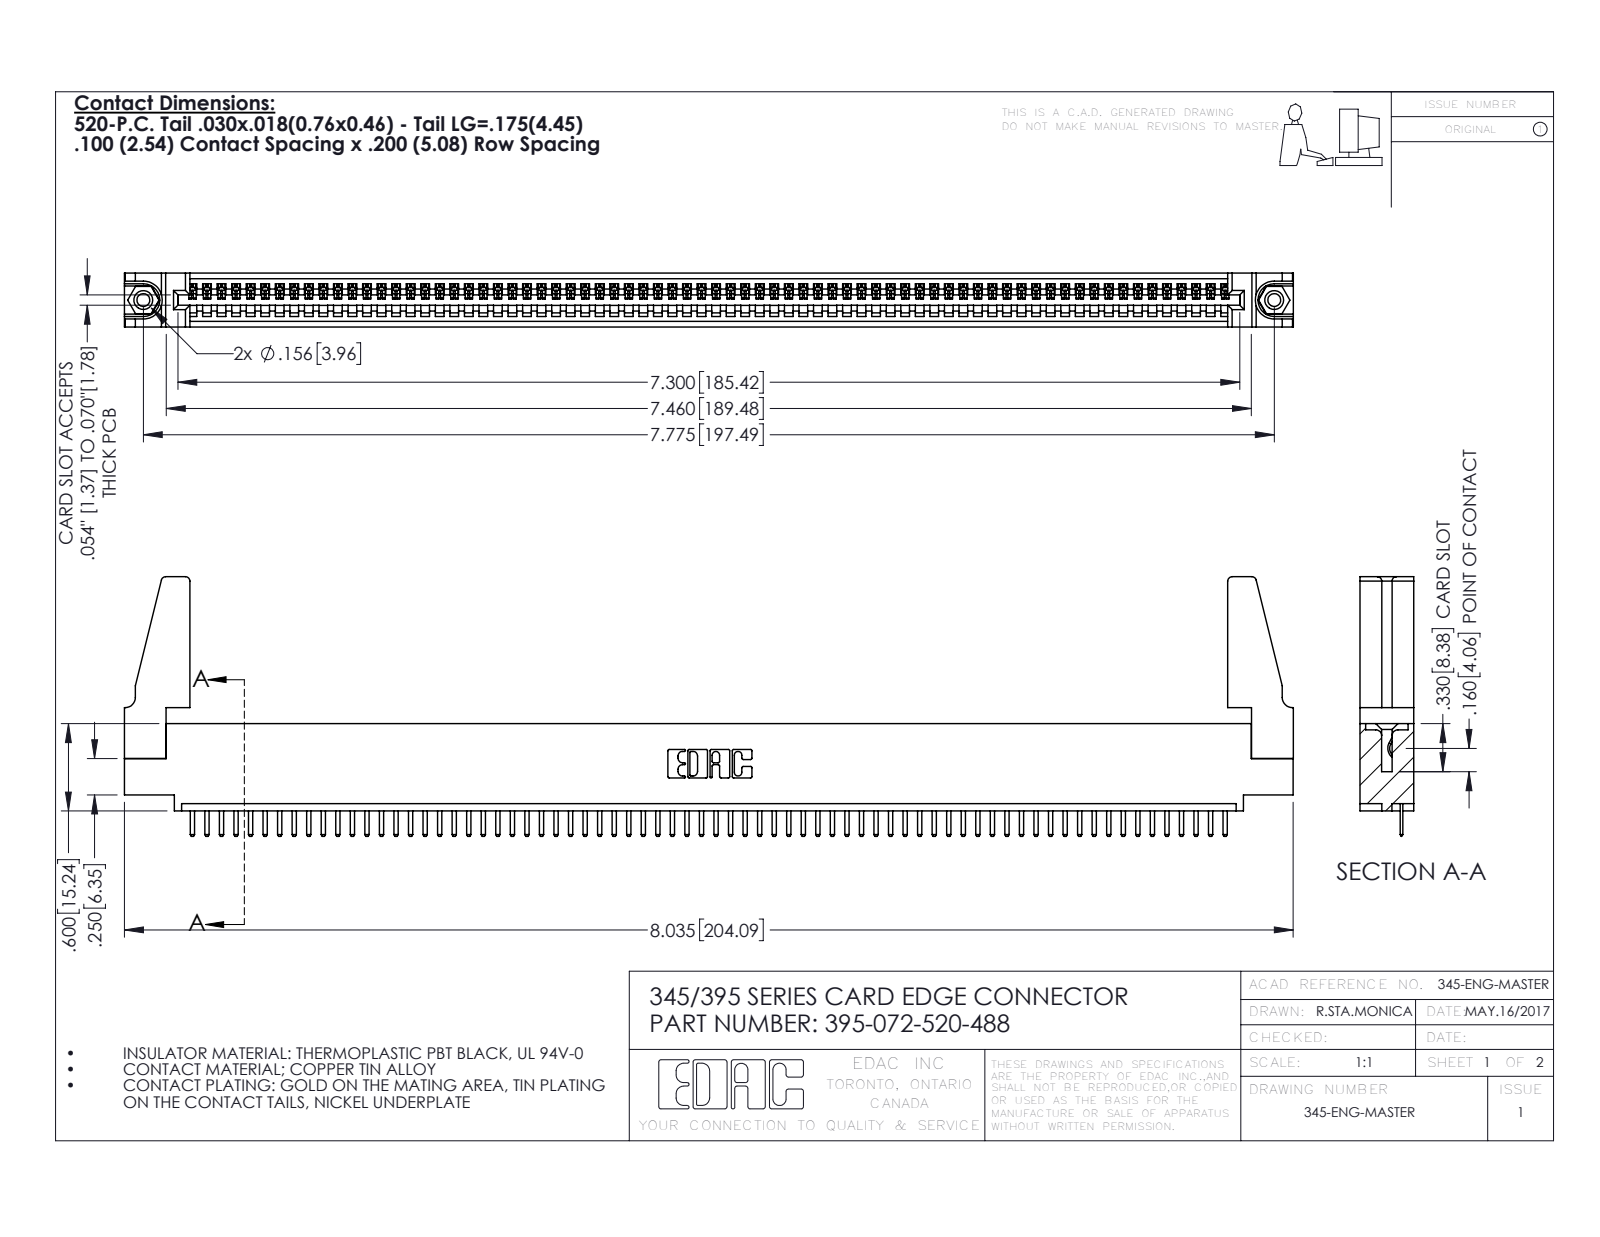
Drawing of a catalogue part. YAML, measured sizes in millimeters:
part_name: "345-220-078_345-220-088; 345 Part_0.110 Offset - 0.156 Dia-TH; 345-250-001_345-250-001-102; 345-292-001_345-293-120 (+1 more)"
step_written_by: "SolidWorks 2016 (CONFIG_CONTROL_DESIGN)"
units: millimeters
bodies: {solids: 77, faces: 4718, planar: 3180, cylindrical: 1522, other: 16}
overall_size: [204.1, 45.3, 9.4]
volume: 22600
surface_area: 28660
round_holes:
  - {diameter: 2.3, count: 2}
  - {diameter: 3.2, count: 2}
  - {diameter: 4, count: 2}
  - {diameter: 1.6, count: 1}
round_bosses_or_shafts:
  - {diameter: 3.9, count: 2}
partial_cylinders:
  - {radius: 0.3, count: 146}
  - {radius: 0.2, count: 144}
  - {radius: 0.3, count: 22}
  - {radius: 0.8, count: 8}
  - {radius: 0.2, count: 6}
  - {radius: 0.8, count: 6}
  - {radius: 0.7, count: 3}
  - {radius: 0.8, count: 2}
face_to_face_distances: [1.8, 7.6, 9.4, 5.1, 2.5, 6.9, 0.6, 5.7, 1.8, 3.8]
hole_center_spacings: [6.9, 191.5, 197.5]
